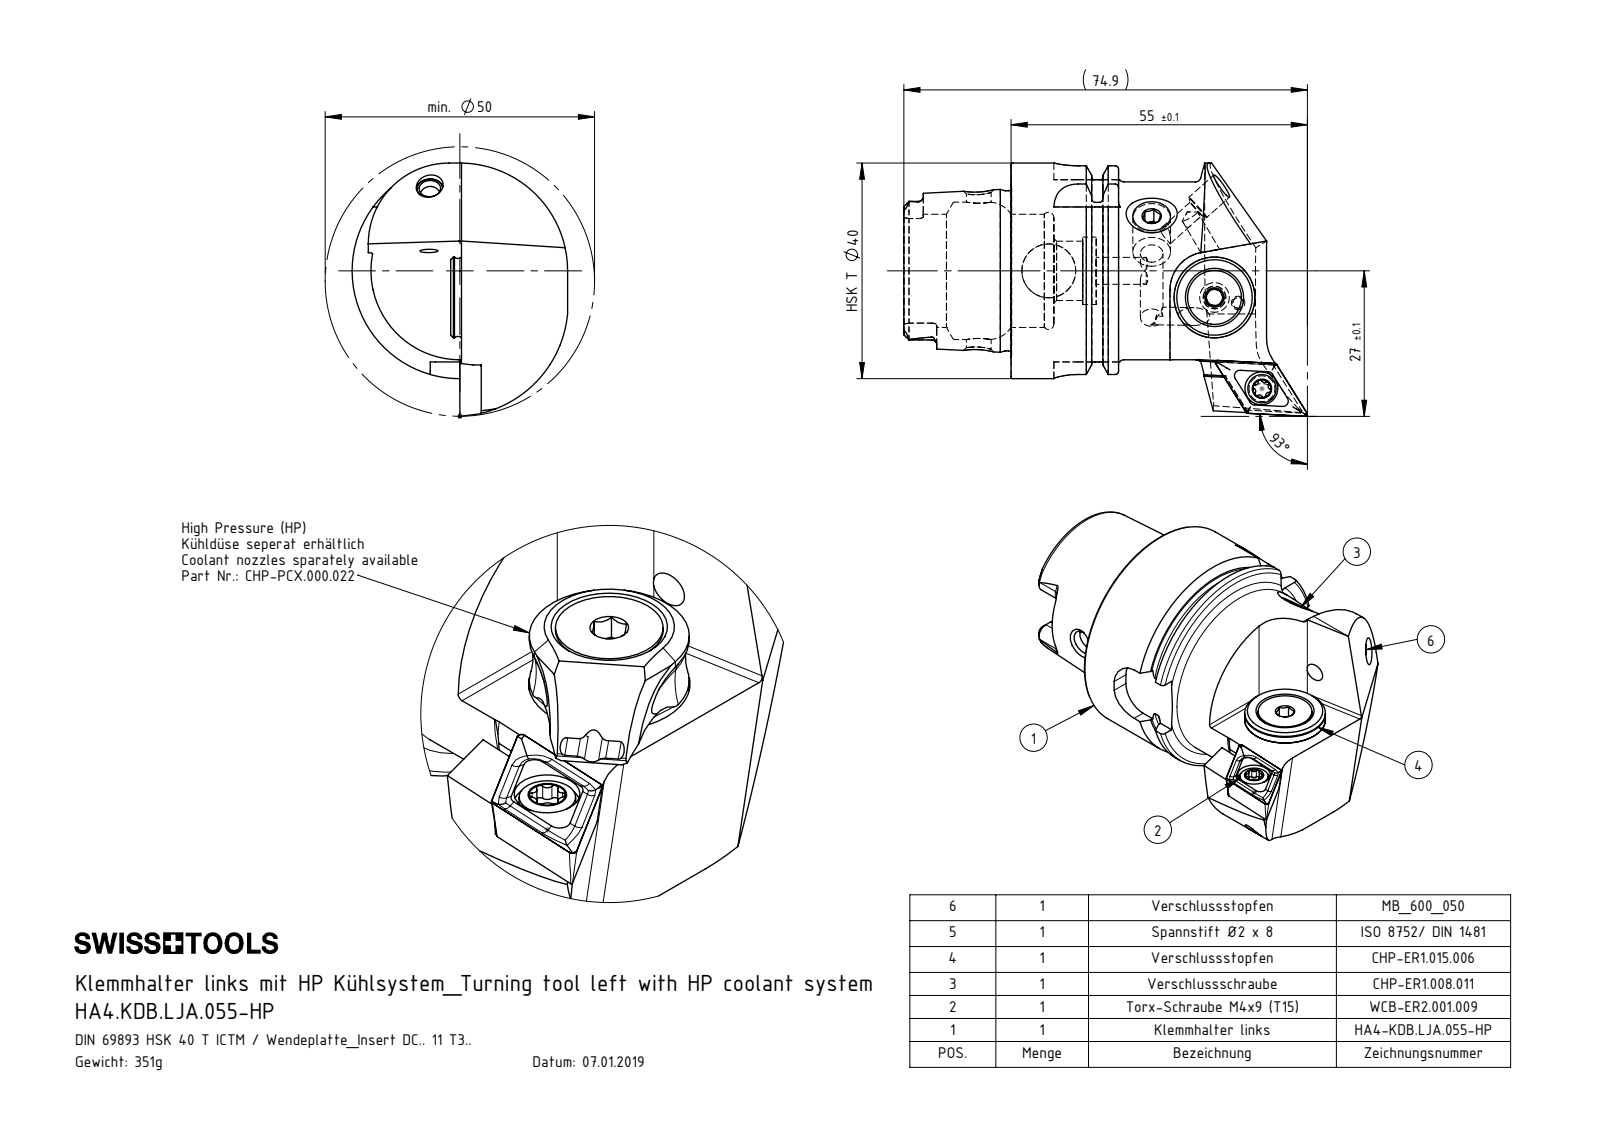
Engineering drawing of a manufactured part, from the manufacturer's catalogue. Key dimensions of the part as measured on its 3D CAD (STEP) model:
Part name (STEP PRODUCT): CHP-ER1.015.006_A; DCMT11T304; CHP-ER1.015.006; HA4-KDB.LJA.055-HP_A_Fertigbearbeitung (+7 more)
STEP written by: SolidWorks 2017 (AUTOMOTIVE_DESIGN)
Units: millimetres
Bodies: 10 solids, 334 faces (123 planar, 81 cylindrical, 130 other)
Overall size (bounding box): 74.91 × 47 × 40
Volume: 44 430 mm³ · Surface area: 16 990 mm²
Round holes (diameter × count): ⌀3.3 ×4, ⌀4.2 ×2, ⌀5 ×2, ⌀1.2 ×1, ⌀2 ×1, ⌀2.5 ×1, ⌀3 ×1, ⌀4 ×1, ⌀4.4 ×1, ⌀4.6 ×1, ⌀5.2 ×1, ⌀6.1 ×1
Round bosses / shafts (diameter × count): ⌀5 ×2, ⌀40 ×1, ⌀34.75 ×1, ⌀33 ×1, ⌀29.71 ×1, ⌀15 ×1, ⌀13.4 ×1, ⌀10 ×1
Partial cylindrical surfaces — rounded edges, fillets, slot ends (radius × count): R0.34 ×6, R0.59 ×6, R0.9 ×6, R4.5 ×4, R0.5 ×2, R1.82 ×2, R1.88 ×2, R7 ×2
Main face-to-face distances: 4.5, 7.95, 19.95, 12, 0.83, 3.67, 29.5, 21.55, 9.55, 19.9
Hole centre spacings: 4.5, 16.43, 16.52, 18.97, 19.09, 31.15, 35.65, 45.08
